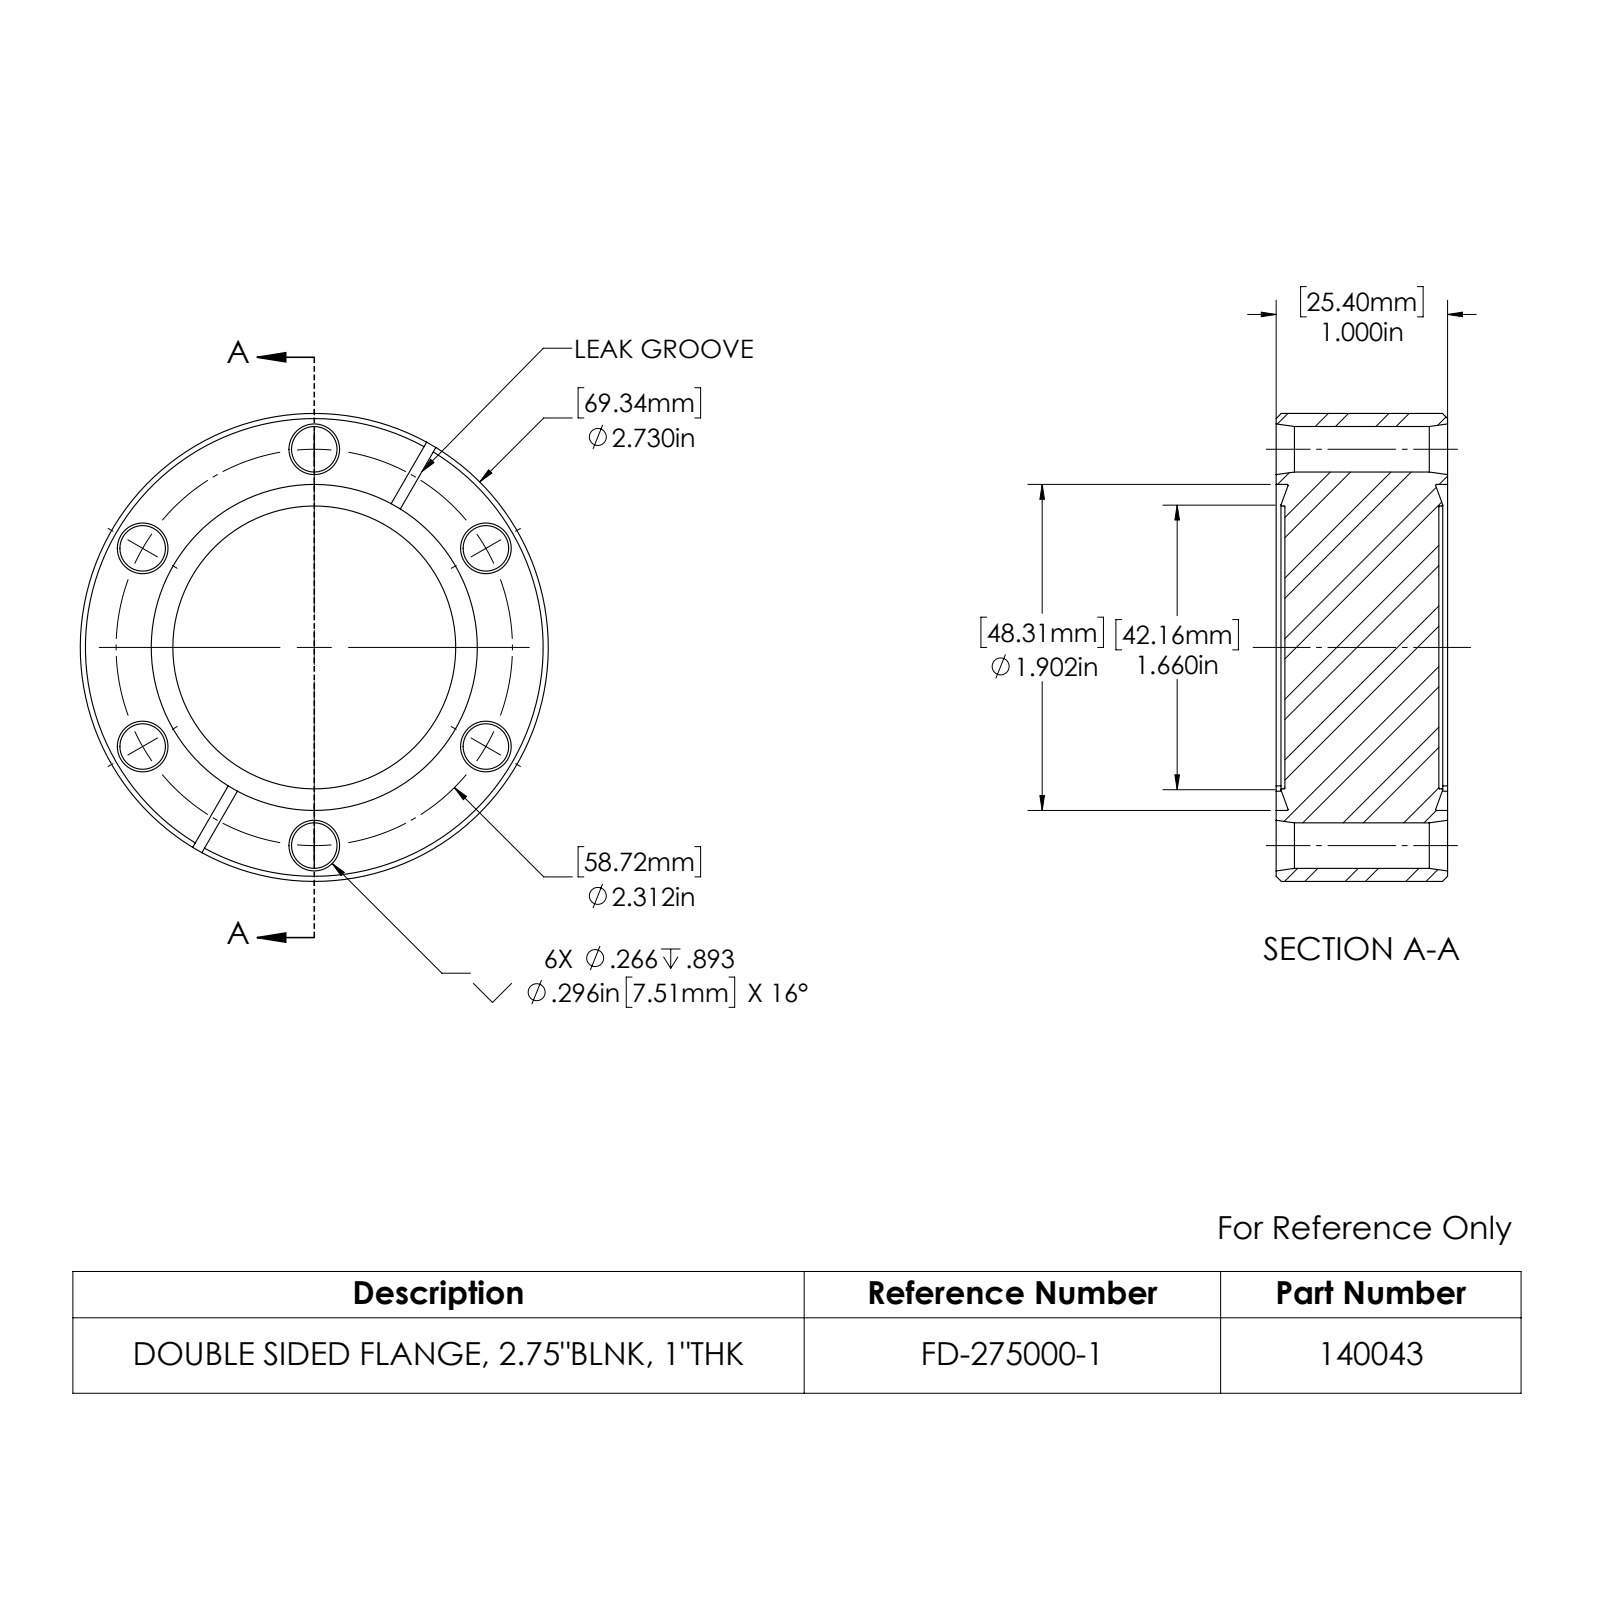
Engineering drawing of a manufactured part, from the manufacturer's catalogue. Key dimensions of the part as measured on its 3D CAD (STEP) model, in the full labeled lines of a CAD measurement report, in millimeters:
Part name (STEP PRODUCT): 140043_A
STEP written by: SolidWorks 2022 (CONFIG_CONTROL_DESIGN)
Units: millimetres
Bodies: 1 solid, 86 faces (14 planar, 26 cylindrical, 46 other)
Overall size (bounding box): 69.3 × 69.3 × 25.4
Volume: 85 310 mm³ · Surface area: 16 540 mm²
Round holes (diameter × count): ⌀6.8 ×6, ⌀41.9 ×1, ⌀48.3 ×1
Round bosses / shafts (diameter × count): ⌀69.3 ×1
Partial cylindrical surfaces — rounded edges, fillets, slot ends (radius × count): R31.8 ×4
Main face-to-face distances: 1.3, 24.1, 25.4, 22.8, 1.6
Hole centre spacings: 29.4, 50.9, 50.9, 58.7, 58.7
